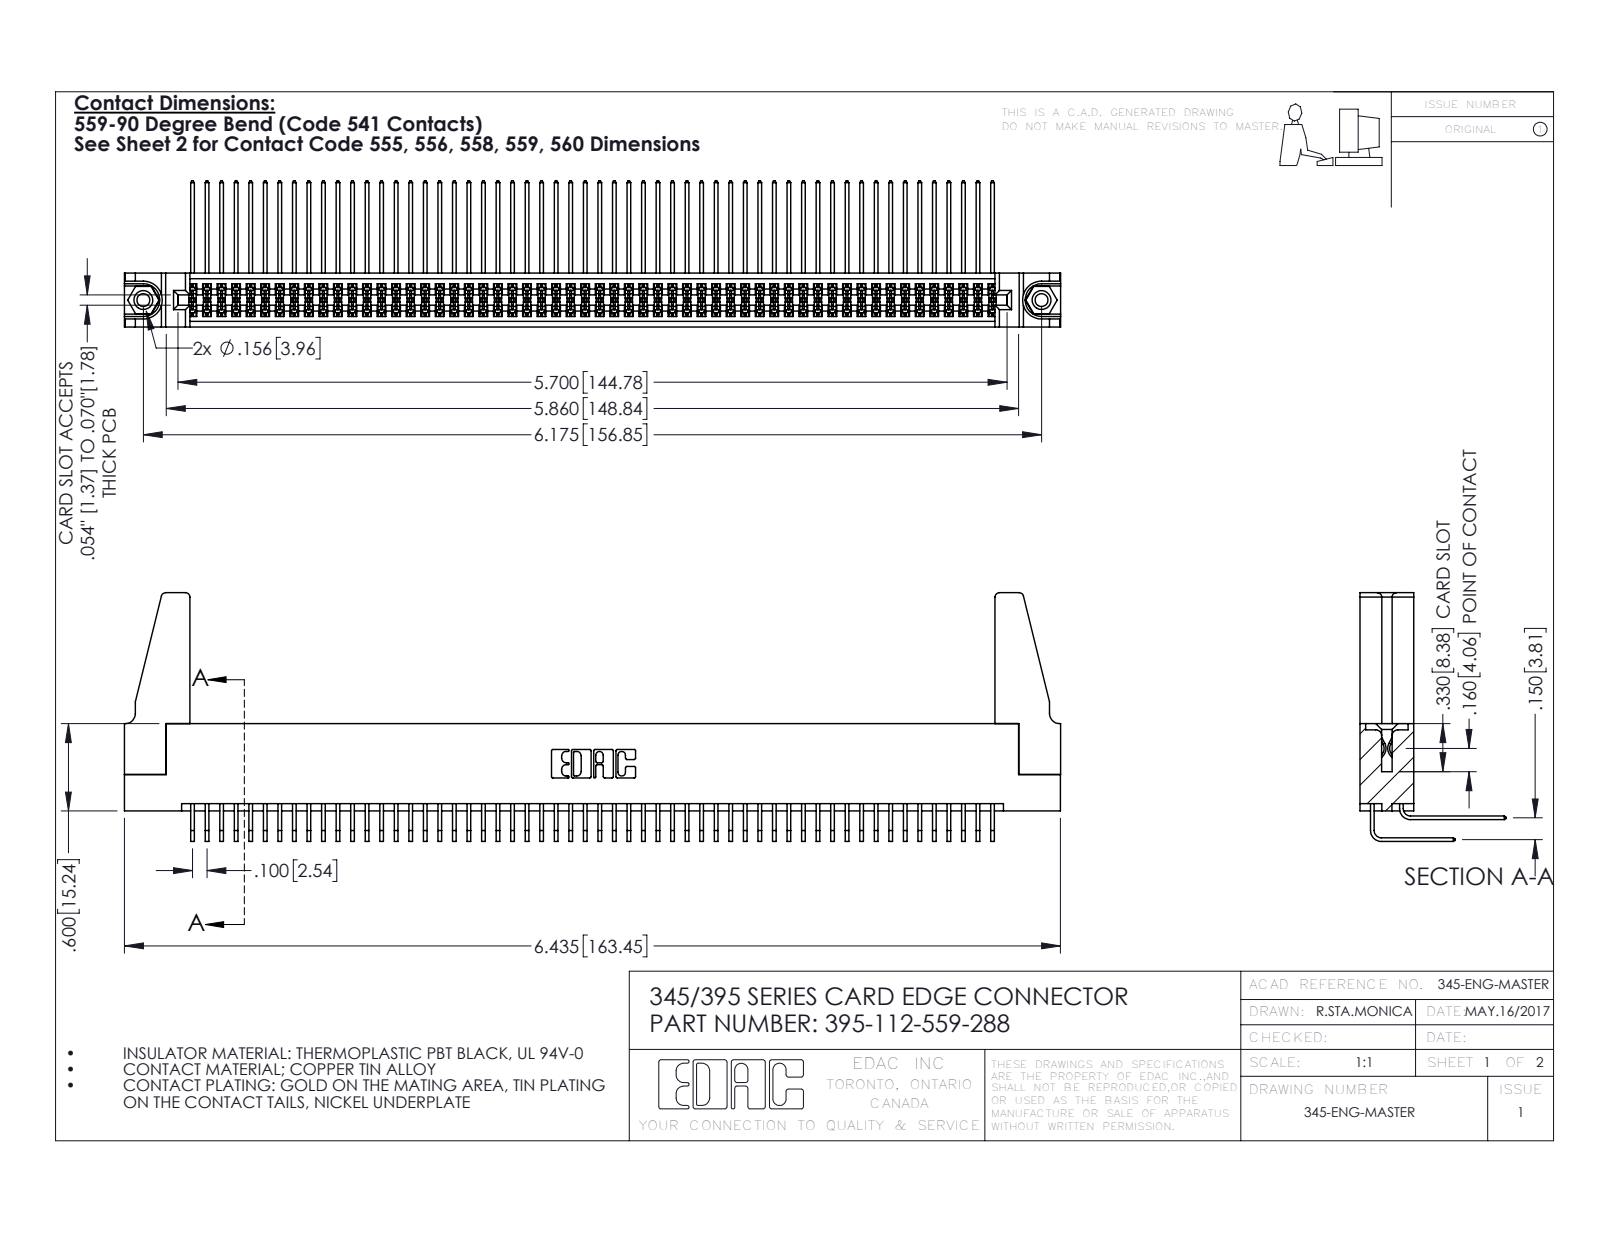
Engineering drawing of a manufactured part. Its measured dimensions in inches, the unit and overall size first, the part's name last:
Units: inches
Overall size (bounding box): 6.436 × 1.709 × 1.005
Round holes (diameter × count): ⌀0.089 ×2, ⌀0.125 ×2, ⌀0.156 ×2, ⌀0.064 ×1
Round bosses / shafts (diameter × count): ⌀0.155 ×2
Partial cylindrical surfaces — rounded edges, fillets, slot ends (radius × count): R0.006 ×168, R0.01 ×22, R0.03 ×8, R0.007 ×6, R0.031 ×6, R0.026 ×3, R0.014 ×2, R0.019 ×2
Main face-to-face distances: 0.072, 0.298, 0.37, 0.2, 0.098, 0.272, 0.025, 0.225, 0.175, 0.15
Hole centre spacings: 0.27, 5.939, 6.175
Volume: 1.215 in³ · Surface area: 48.13 in²
Bodies: 117 solids, 6074 faces (4072 planar, 1986 cylindrical, 16 other)
Part name (STEP PRODUCT): 345-250-001_345-250-001-102; 345-292-001_559 Tail - 2; 345 Part_Flush Mounting Lugs - 0.156 Dia-TH; 345-292-001_558 559 Tail - 1 (+2 more)
STEP written by: SolidWorks 2016 (CONFIG_CONTROL_DESIGN)
